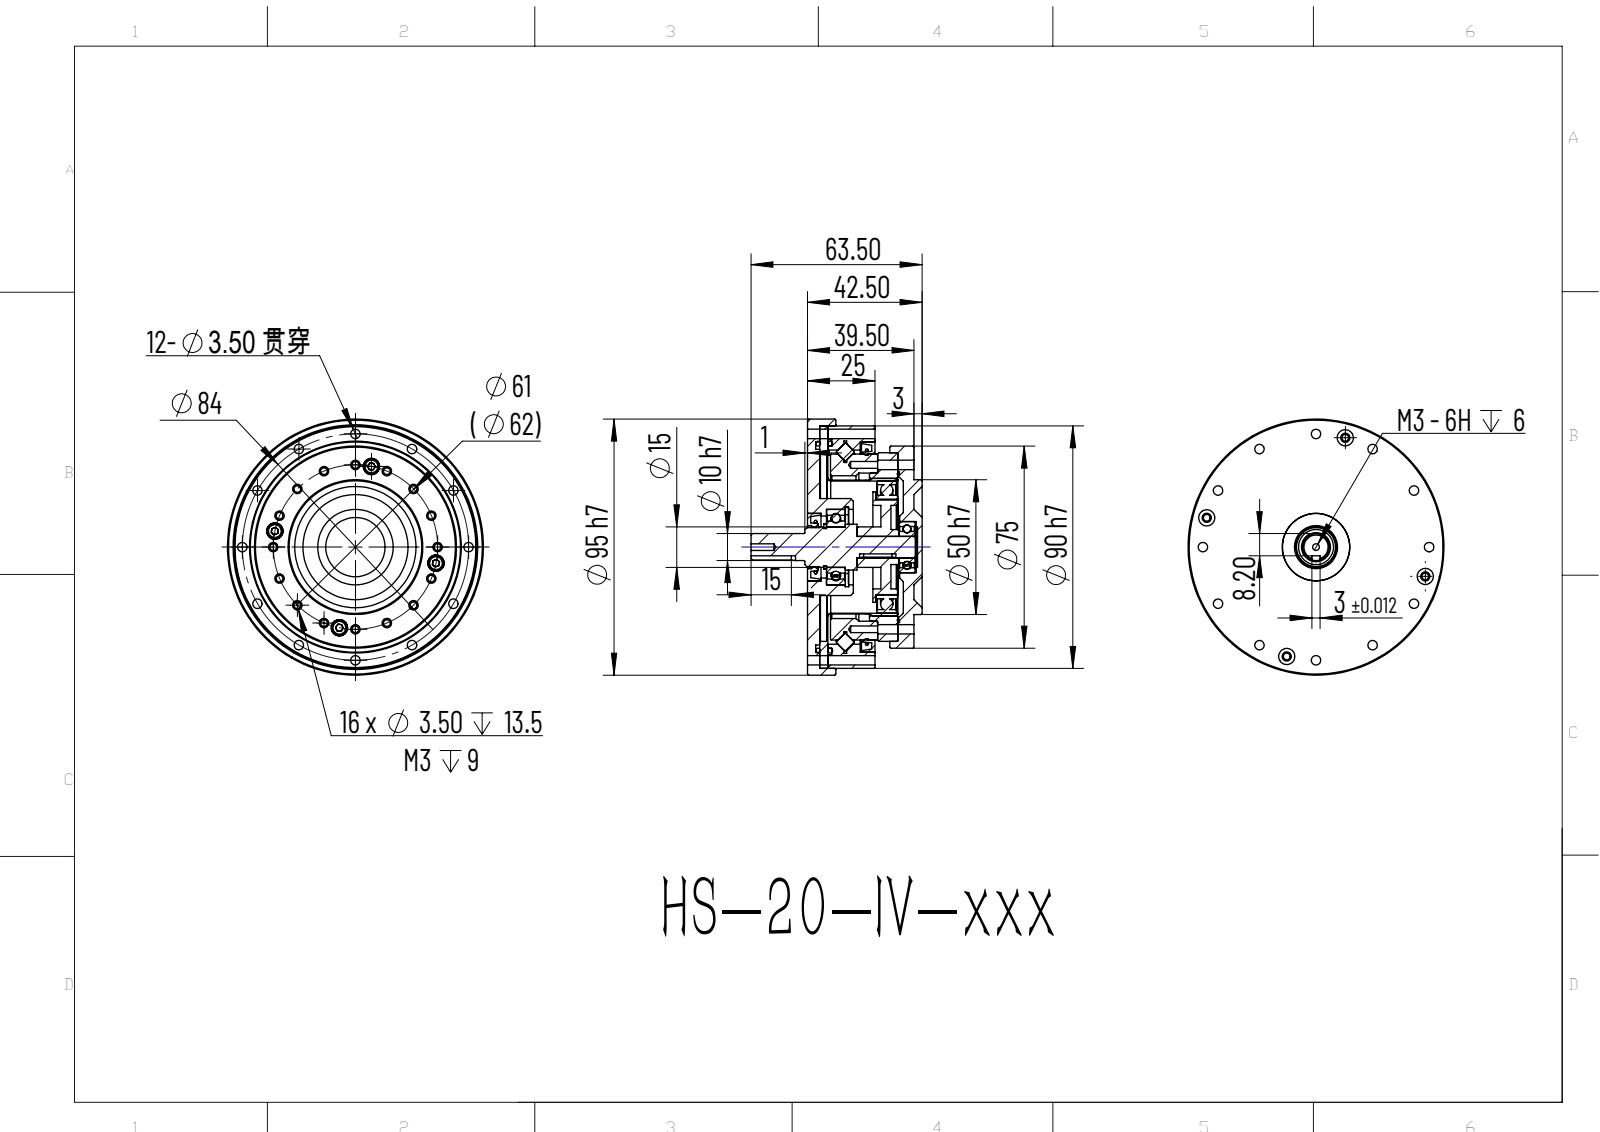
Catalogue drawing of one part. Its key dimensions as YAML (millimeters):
part_name: "HS-20-IV; ?????619?8-2RS]_??; ??????61902-2RS]_??; ????25??15?5 (+8 more)"
step_written_by: "ONSHAPE BY PTC INC, 1.201 (AP242_MANAGED_MODEL_BASED_3D_ENGINEERING_MIM_LF)"
units: millimeters
bodies: {solids: 129, faces: 1434, planar: 620, cylindrical: 448, other: 366}
overall_size: [95, 95, 63.5]
volume: 169125
surface_area: 132070
round_holes:
  - {diameter: 3.5, count: 32}
  - {diameter: 2.5, count: 27}
  - {diameter: 3.4, count: 8}
  - {diameter: 6, count: 8}
  - {diameter: 1.7, count: 2}
  - {diameter: 2, count: 2}
  - {diameter: 2.05, count: 1}
  - {diameter: 2.9, count: 1}
  - {diameter: 5, count: 1}
  - {diameter: 8, count: 1}
  - {diameter: 12.95, count: 1}
  - {diameter: 13.8, count: 1}
round_bosses_or_shafts:
  - {diameter: 5, count: 36}
  - {diameter: 5.5, count: 4}
  - {diameter: 3, count: 4}
  - {diameter: 95, count: 1}
  - {diameter: 90, count: 1}
  - {diameter: 75, count: 1}
  - {diameter: 72.6, count: 1}
  - {diameter: 69, count: 1}
partial_cylinders:
  - {radius: 2.52, count: 36}
  - {radius: 1.5, count: 3}
  - {radius: 0.2, count: 2}
  - {radius: 0.5, count: 2}
  - {radius: 2.8, count: 2}
  - {radius: 8.4, count: 1}
  - {radius: 10.5, count: 1}
  - {radius: 12.85, count: 1}
face_to_face_distances: [3, 7.5, 4.5, 26, 17.5, 25, 6, 8.5, 1, 35]
hole_center_spacings: [30.5, 11.9, 33.89, 43.13, 56.36, 59.83, 23.35, 5.98]
